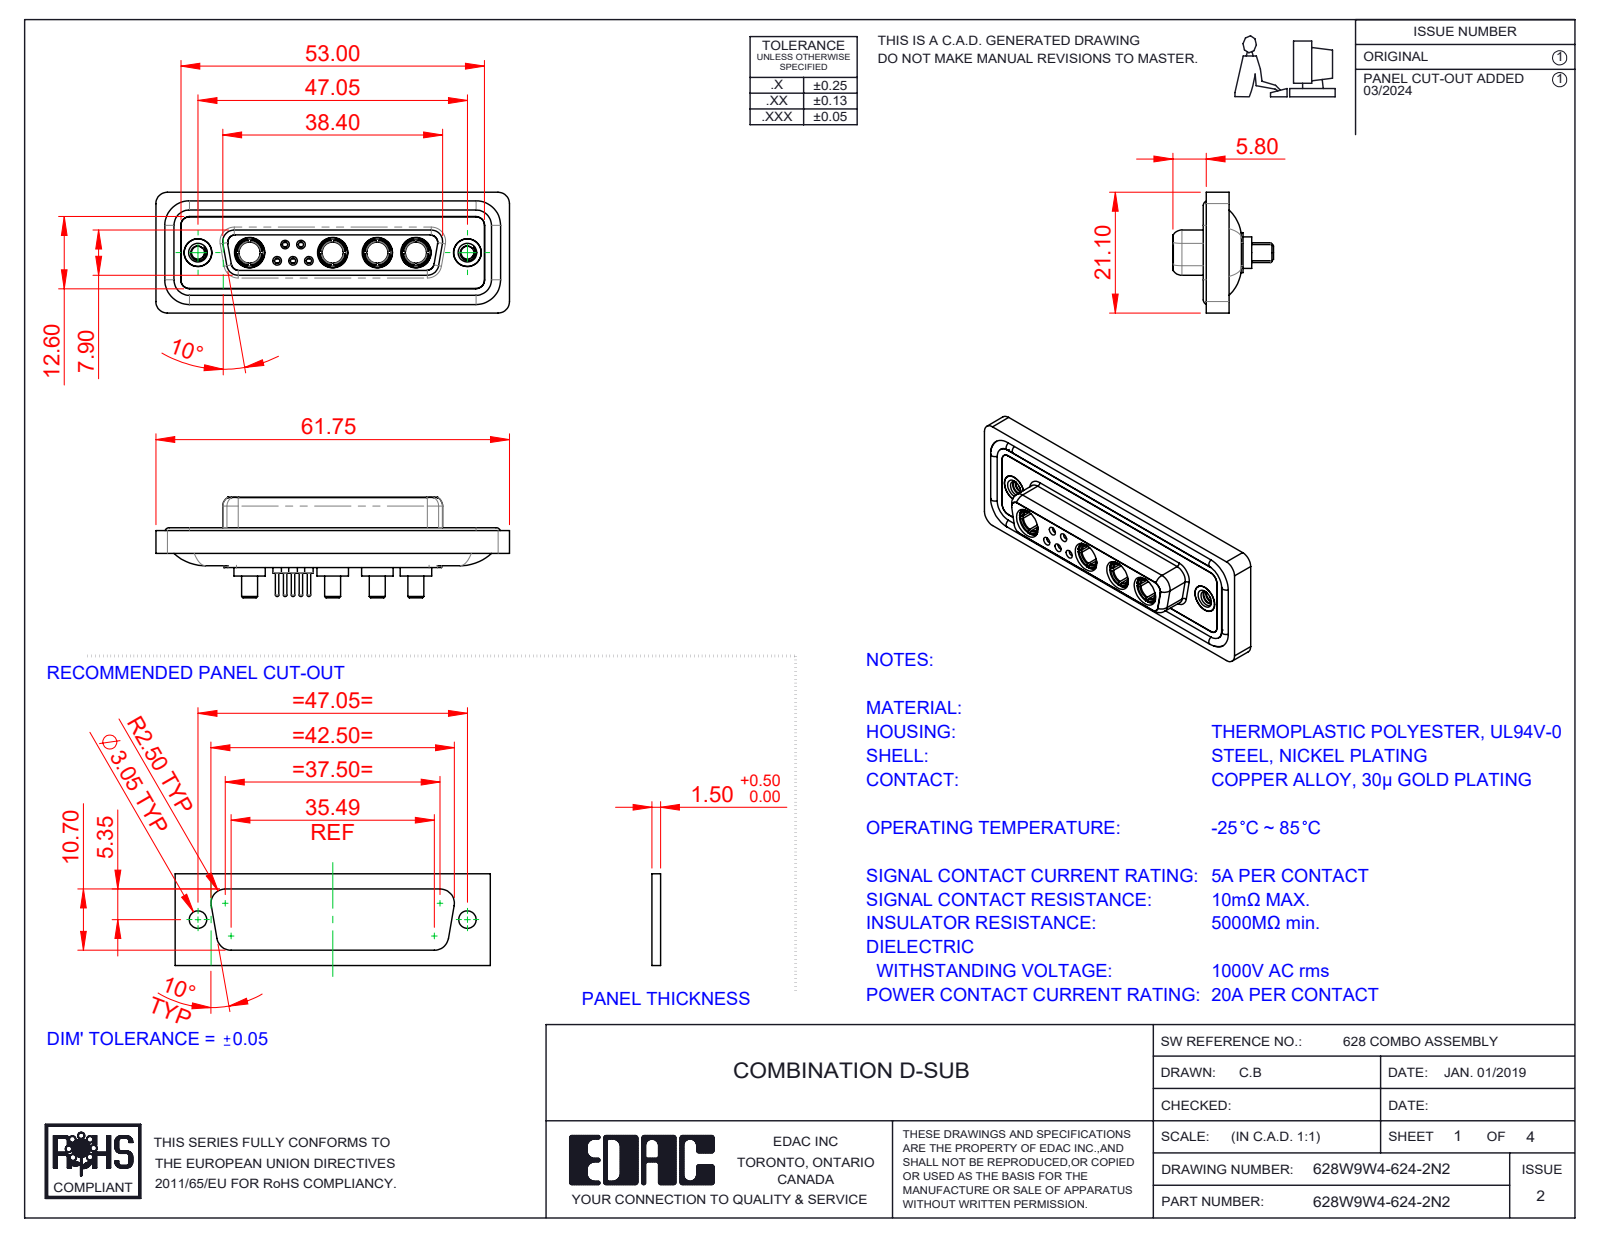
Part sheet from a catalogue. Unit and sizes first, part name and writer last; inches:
Units: inches
Overall size (bounding box): 2.431 × 0.831 × 0.691
Round holes (diameter × count): ⌀0.191 ×6, ⌀0.035 ×5, ⌀0.043 ×5, ⌀0.059 ×5, ⌀0.079 ×5, ⌀0.146 ×4, ⌀0.209 ×4, ⌀0.063 ×3, ⌀0.067 ×2, ⌀0.089 ×2, ⌀0.157 ×2, ⌀0.159 ×2
Round bosses / shafts (diameter × count): ⌀0.063 ×6, ⌀0.087 ×5, ⌀0.024 ×5, ⌀0.217 ×4, ⌀0.205 ×4, ⌀0.195 ×4, ⌀0.187 ×4, ⌀0.148 ×4
Partial cylindrical surfaces — rounded edges, fillets, slot ends (radius × count): R0.059 ×22, R0.079 ×18, R0.053 ×8, R0.063 ×8, R0.01 ×4, R0.02 ×4, R0.024 ×4, R0.026 ×4
Main face-to-face distances: 0.016, 0.071, 0.293, 0.222, 0.02, 0.278, 0.26, 0.063, 0.043, 0.114
Hole centre spacings: 0.124, 0.109, 0.198, 0.109, 0.173, 0.198, 0.218, 0.226
Volume: 0.502 in³ · Surface area: 21.02 in²
Bodies: 20 solids, 957 faces (296 planar, 375 cylindrical, 286 other)
Part name (STEP PRODUCT): 628Combo Shell Front_25 Contacts; 628Combo Shell Rear_25 Contacts; 628Combo Contact Row 2_24; 628Combo Threaded Rivet_2 (+5 more)
STEP written by: SolidWorks 2023 (CONFIG_CONTROL_DESIGN)
